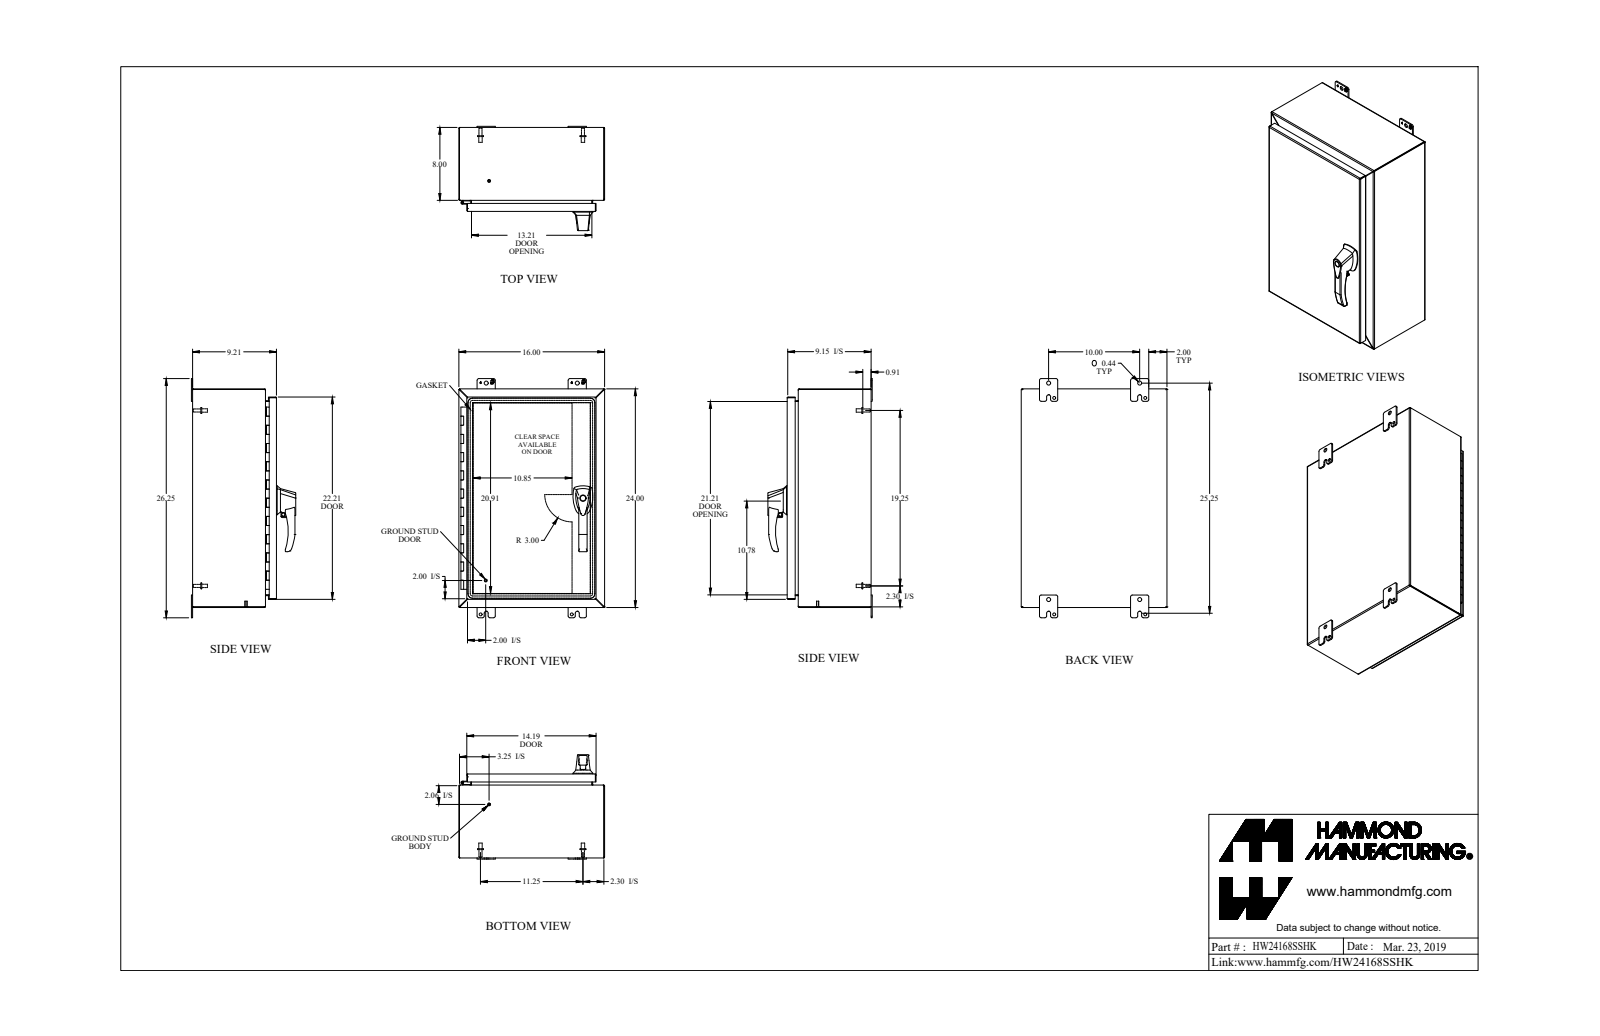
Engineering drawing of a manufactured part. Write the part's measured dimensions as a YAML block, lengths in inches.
part_name: "HW24168SSHK"
step_written_by: "SolidWorks 2018 (AUTOMOTIVE_DESIGN)"
units: inches
bodies: {solids: 47, faces: 1618, planar: 776, cylindrical: 573, other: 269}
overall_size: [26.25, 16, 11.45]
volume: 145.9
surface_area: 3688
round_holes:
  - {diameter: 0.176, count: 6}
  - {diameter: 0.313, count: 5}
  - {diameter: 0.25, count: 3}
  - {diameter: 0.413, count: 3}
  - {diameter: 0.196, count: 2}
  - {diameter: 0.256, count: 2}
  - {diameter: 0.265, count: 2}
  - {diameter: 0.394, count: 2}
  - {diameter: 0.437, count: 2}
  - {diameter: 0.187, count: 1}
  - {diameter: 0.233, count: 1}
  - {diameter: 0.265, count: 1}
round_bosses_or_shafts:
  - {diameter: 0.375, count: 10}
  - {diameter: 0.25, count: 7}
  - {diameter: 0.156, count: 6}
  - {diameter: 0.65, count: 4}
  - {diameter: 0.332, count: 4}
  - {diameter: 0.313, count: 4}
  - {diameter: 1, count: 3}
  - {diameter: 0.51, count: 3}
partial_cylinders:
  - {radius: 0.25, count: 27}
  - {radius: 0.188, count: 24}
  - {radius: 0.036, count: 20}
  - {radius: 0.108, count: 20}
  - {radius: 0.06, count: 12}
  - {radius: 0.125, count: 9}
  - {radius: 0.045, count: 8}
  - {radius: 0.218, count: 8}
face_to_face_distances: [0.072, 0.072, 15.928, 9.138, 9.066, 9.138, 9.21, 23.928, 15.856, 7.928]
hole_center_spacings: [1.111, 8.118, 8.119, 16.237, 1.338, 6.78, 7.576, 7.577]
